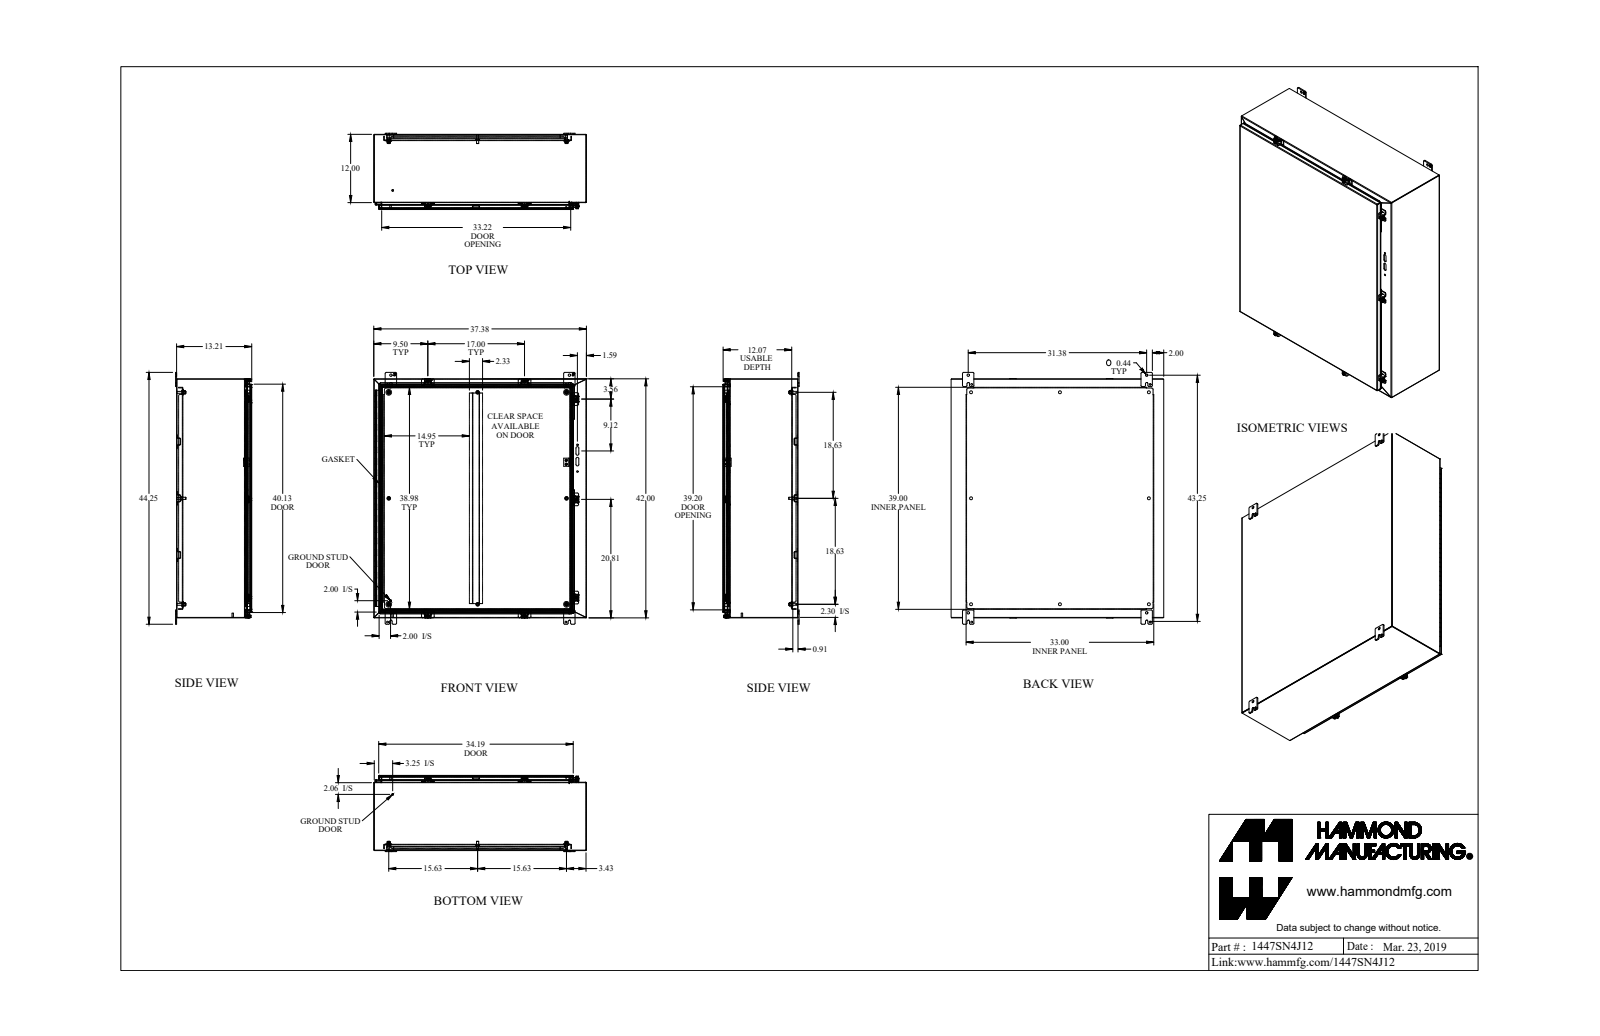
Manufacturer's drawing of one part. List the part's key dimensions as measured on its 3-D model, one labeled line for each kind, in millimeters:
Part name (STEP PRODUCT): 1447SN4J12_Default
STEP written by: SolidWorks 2019 (CONFIG_CONTROL_DESIGN)
Units: millimetres
Bodies: 68 solids, 2230 faces (1294 planar, 805 cylindrical, 131 other)
Overall size (bounding box): 1124 × 949.3 × 340.3
Volume: 9 423 000 mm³ · Surface area: 9 728 000 mm²
Round holes (diameter × count): ⌀12.7 ×8, ⌀5.4 ×7, ⌀6.7 ×7, ⌀9.5 ×7, ⌀8 ×6, ⌀7.8 ×4, ⌀11.1 ×4, ⌀11.3 ×4, ⌀3.8 ×2, ⌀4 ×2, ⌀7.1 ×2, ⌀4.7 ×1
Round bosses / shafts (diameter × count): ⌀16.5 ×8, ⌀9.5 ×8, ⌀8.4 ×8, ⌀12.7 ×7, ⌀9.9 ×7, ⌀6.2 ×7, ⌀25.4 ×4, ⌀6.4 ×4
Partial cylindrical surfaces — rounded edges, fillets, slot ends (radius × count): R6.4 ×44, R4.8 ×35, R1.2 ×33, R3.6 ×33, R0.9 ×21, R2.7 ×21, R2.9 ×16, R3.6 ×14
Main face-to-face distances: 1.8, 331.9, 333.7, 1.8, 333.7, 335.5, 2.4, 307.5, 305.7, 26.2
Hole centre spacings: 793.8, 1235, 946.2, 182.8, 194.9, 396.9, 396.9, 473.1
